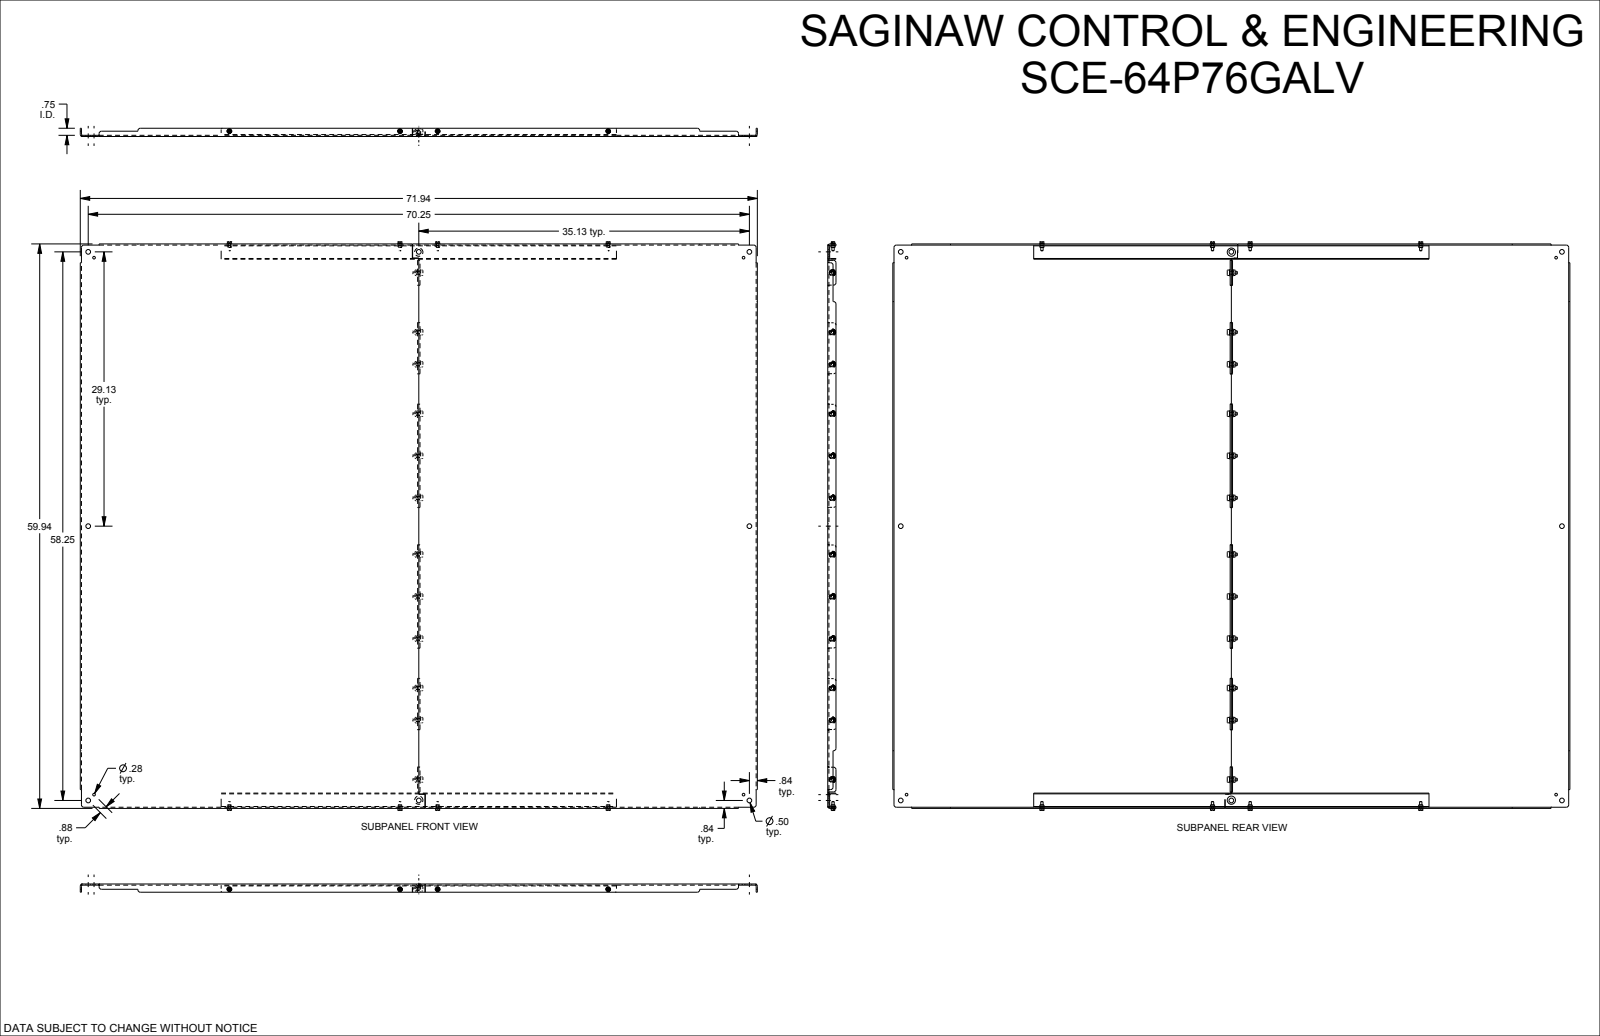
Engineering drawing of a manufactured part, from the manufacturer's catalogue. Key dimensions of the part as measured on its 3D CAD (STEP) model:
Part name (STEP PRODUCT): SCE-64P76GALV
STEP written by: SolidWorks 2019 (CONFIG_CONTROL_DESIGN)
Units: inches
Bodies: 44 solids, 1922 faces (528 planar, 478 cylindrical, 916 other)
Overall size (bounding box): 71.938 × 60.386 × 0.875
Volume: 584.6 in³ · Surface area: 9 605 in²
Round holes (diameter × count): ⌀0.312 ×12, ⌀0.375 ×12, ⌀0.5 ×8, ⌀0.25 ×4, ⌀0.308 ×4, ⌀0.344 ×4, ⌀0.281 ×3, ⌀0.875 ×2, ⌀0.28 ×1
Round bosses / shafts (diameter × count): ⌀0.31 ×12, ⌀0.5 ×4, ⌀0.44 ×4, ⌀0.343 ×4, ⌀0.248 ×4
Partial cylindrical surfaces — rounded edges, fillets, slot ends (radius × count): R0.01 ×200, R0.25 ×24, R0.06 ×16, R0.172 ×8, R0.112 ×6, R0.237 ×6, R0.08 ×4, R0.158 ×4
Main face-to-face distances: 0.125, 0.125, 0.078, 0.203, 35.844, 1.422, 58.187, 0.078, 59.813, 59.687
Hole centre spacings: 29.125, 0.875, 28.513, 34.511, 34.512, 35.125, 35.125, 45.629
